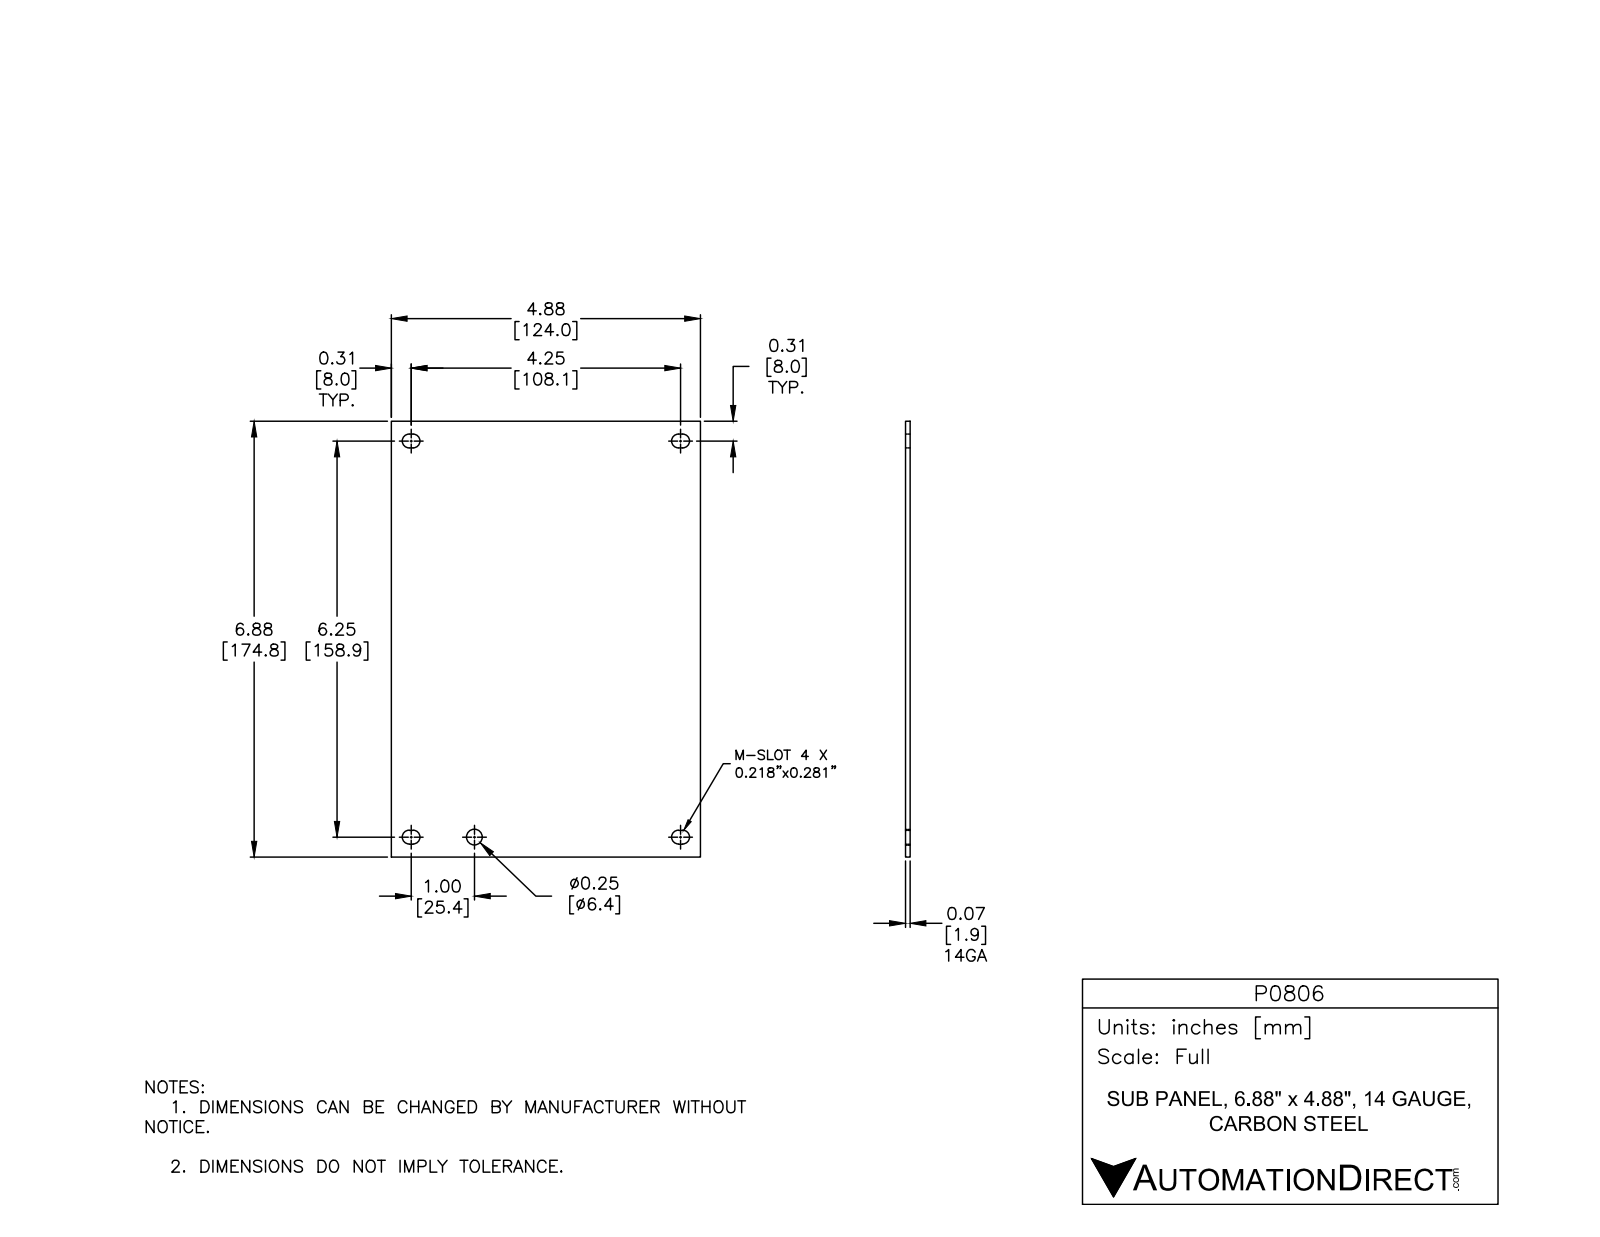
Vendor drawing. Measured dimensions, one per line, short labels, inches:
name: P0806
written by: Autodesk Inventor 2012 (AUTOMOTIVE_DESIGN)
unit: in
bodies: 1 solid, 23 faces (14 planar, 9 cylindrical, 0 other)
size: 6.88 × 4.88 × 0.074
volume: 2.466 in³; area: 68.68 in²
holes: 1× ⌀0.25
rounds: 8× R0.109
face distances: 0.074, 4.88, 6.88, 0.204, 0.422, 6.458, 6.676, 0.218, 6.254, 6.472
